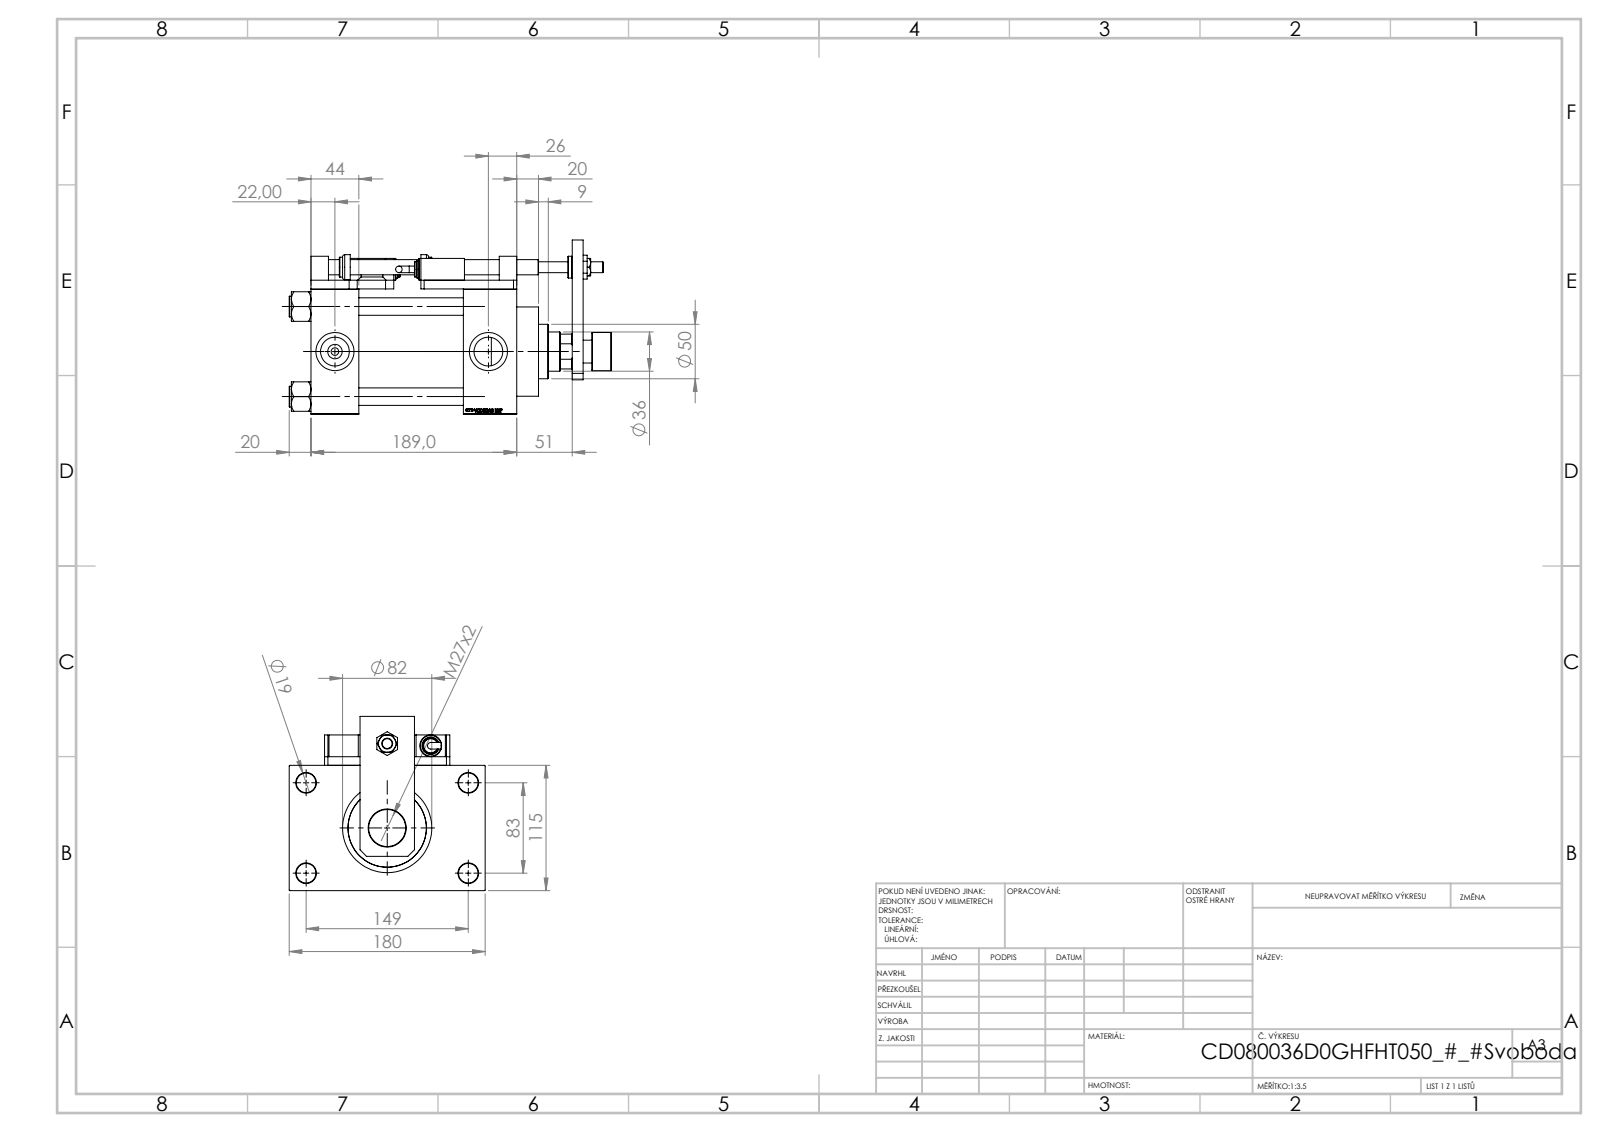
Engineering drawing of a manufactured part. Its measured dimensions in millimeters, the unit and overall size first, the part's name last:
Units: millimetres
Overall size (bounding box): 296 × 180 × 160
Round holes (diameter × count): ⌀8.5 ×4, ⌀13.5 ×4, ⌀16 ×4, ⌀18 ×4, ⌀7 ×2, ⌀26.44 ×2, ⌀35 ×2, ⌀10 ×1, ⌀14 ×1, ⌀25.5 ×1, ⌀27 ×1, ⌀36 ×1
Round bosses / shafts (diameter × count): ⌀19 ×4, ⌀20 ×3, ⌀16 ×2, ⌀14 ×2, ⌀6 ×2, ⌀86 ×1, ⌀82 ×1, ⌀50 ×1
Partial cylindrical surfaces — rounded edges, fillets, slot ends (radius × count): R7.5 ×4
Main face-to-face distances: 115, 8, 145, 49, 44, 189, 96, 140, 123, 32.5
Hole centre spacings: 33.15, 58.48, 82.7, 85.28, 89.24, 115.85, 142.43, 32
Volume: 2 380 000 mm³ · Surface area: 419 778 mm²
Bodies: 25 solids, 1393 faces (670 planar, 160 cylindrical, 563 other)
Part name (STEP PRODUCT): V215CD_SWITCH_Q_TYC; V215CD_SWITCH_Q_PODLOZKA_FRONT; V215CR_ROD_END_F; V215CD_D_TYCINKA (+7 more)
STEP written by: SolidWorks 2019 (CONFIG_CONTROL_DESIGN)
